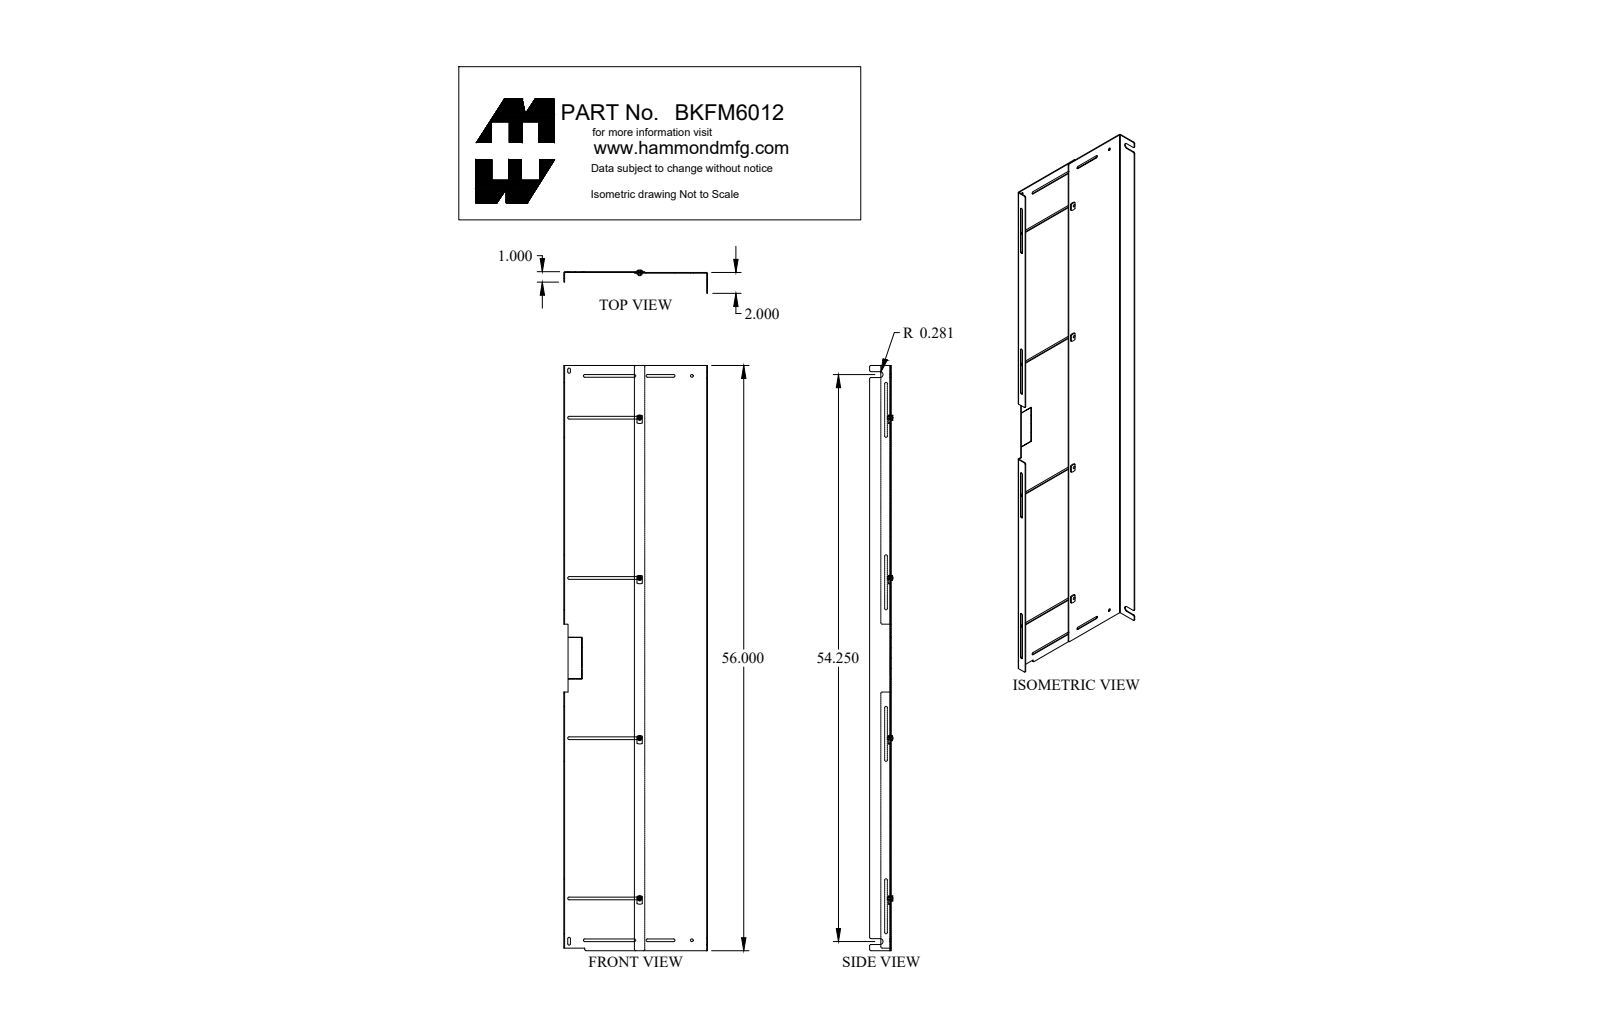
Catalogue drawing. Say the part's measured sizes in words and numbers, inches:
The part is named "BKFM6012_Default". Its 3-D file was written by "SolidWorks 2019 (CONFIG_CONTROL_DESIGN)". It is 10 solids with 317 faces: 158 planar, 115 cylindrical and 44 other. Overall it measures 56 by 13.755 by 2.237 inches. Its volume is 69.01 cubic inches and its surface area 1 947 square inches. Round holes: 4 of diameter 0.201, 4 of diameter 0.313, 2 of diameter 0.26. Round bosses or shafts: 4 of diameter 0.468, 4 of diameter 0.293, 4 of diameter 0.25. Partial cylindrical surfaces (rounded edges, fillets, slot ends): 24 of radius 0.13, 19 of radius 0.125, 8 of radius 0.5, 2 of radius 0.036, 2 of radius 0.108, 2 of radius 0.281. The main face-to-face distances are 0.072, 0.144, 13.683, 13.611, 13.755, 7.75, 7.678, 5.933, 6.005, 6.755. The hole center spacings are 6.403, 15.333, 19.97, 30.667, 35.025, 50.249, 15.333, 46.
